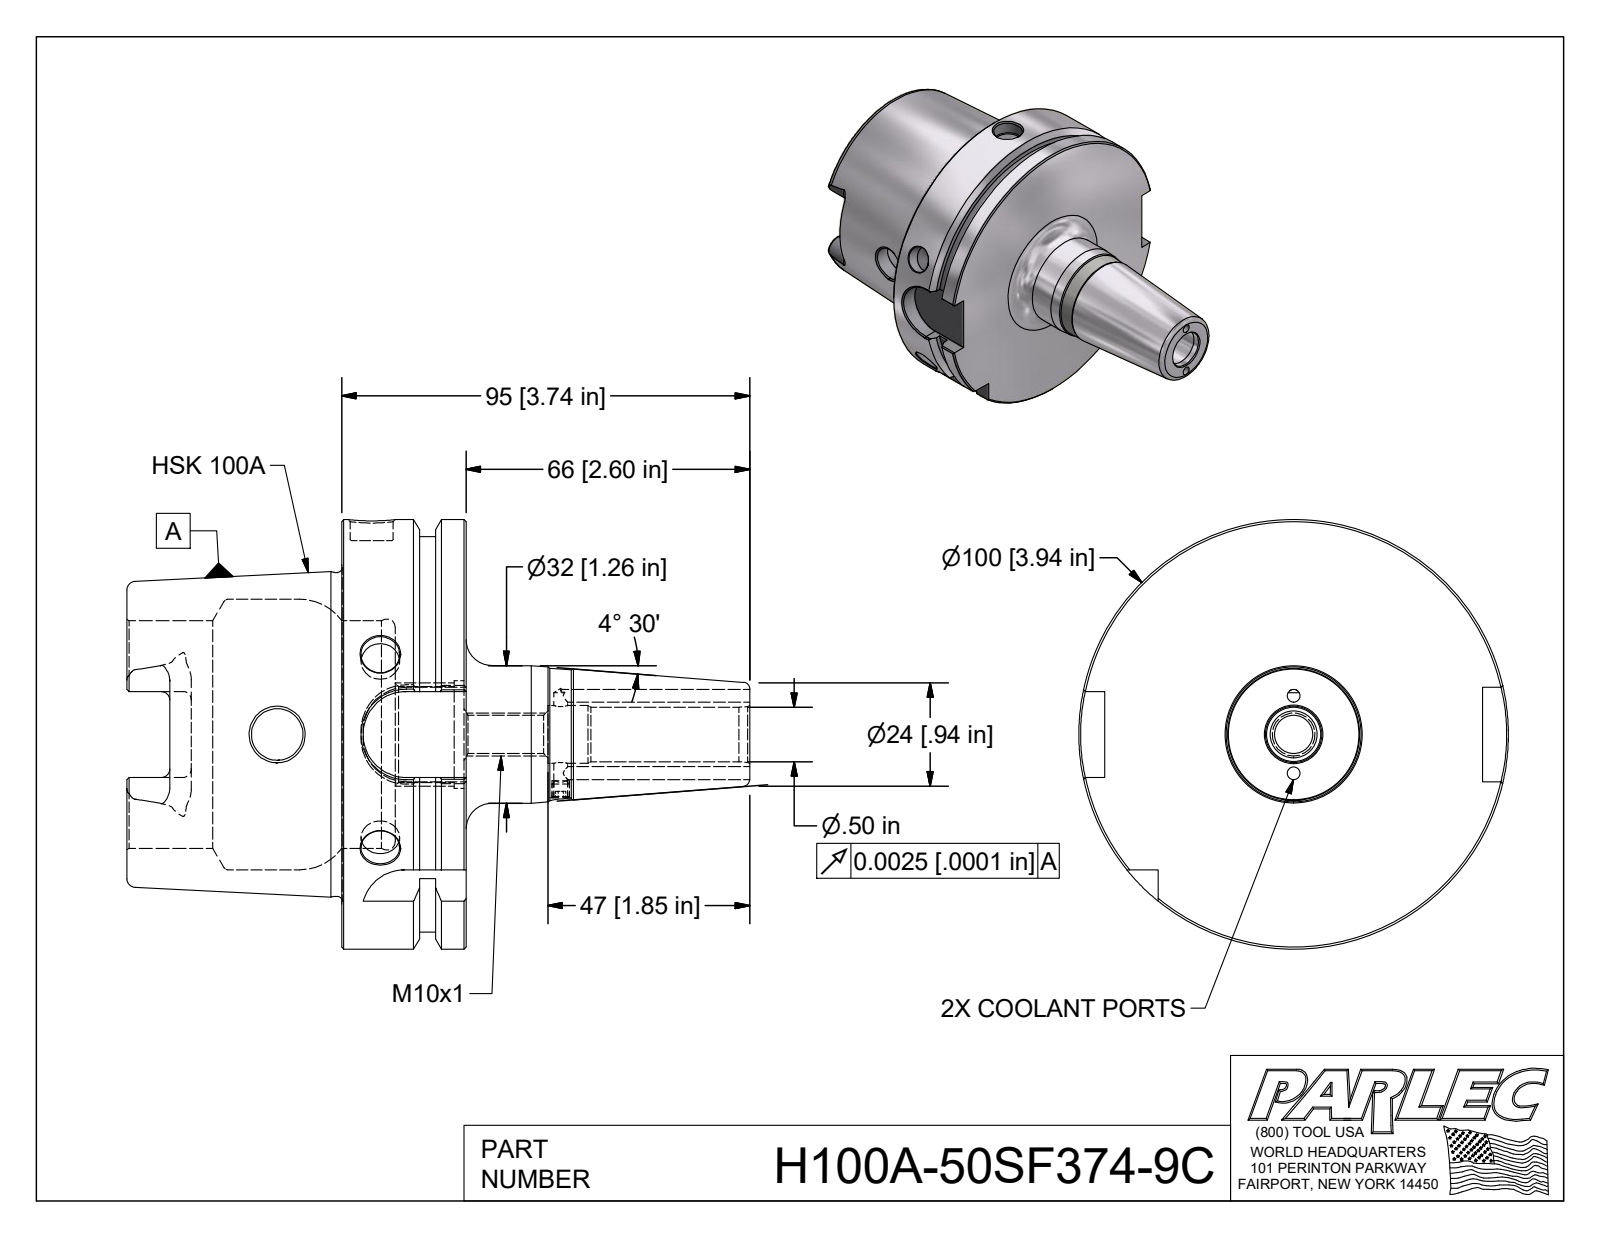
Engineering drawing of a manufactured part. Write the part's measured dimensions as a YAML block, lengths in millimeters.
step_written_by: "Autodesk Inventor 2018 (AUTOMOTIVE_DESIGN)"
units: millimeters
bodies: {solids: 1, faces: 155, planar: 49, cylindrical: 41, other: 65}
overall_size: [145, 100, 100]
volume: 290700
surface_area: 58540
round_holes:
  - {diameter: 3, count: 2}
  - {diameter: 9, count: 2}
  - {diameter: 3.3, count: 1}
  - {diameter: 5, count: 1}
  - {diameter: 6.9, count: 1}
  - {diameter: 10, count: 1}
  - {diameter: 12, count: 1}
  - {diameter: 12.7, count: 1}
  - {diameter: 13.4, count: 1}
  - {diameter: 22.4, count: 1}
  - {diameter: 25, count: 1}
  - {diameter: 53, count: 1}
round_bosses_or_shafts:
  - {diameter: 100, count: 1}
  - {diameter: 92, count: 1}
  - {diameter: 75.4, count: 1}
  - {diameter: 32, count: 1}
partial_cylinders:
  - {radius: 2, count: 6}
  - {radius: 4.9, count: 4}
  - {radius: 10, count: 4}
face_to_face_distances: [29, 12.5, 16.5, 50, 62.5, 79, 88, 71.9, 21.9, 9.4]
hole_center_spacings: [9, 18, 44]
